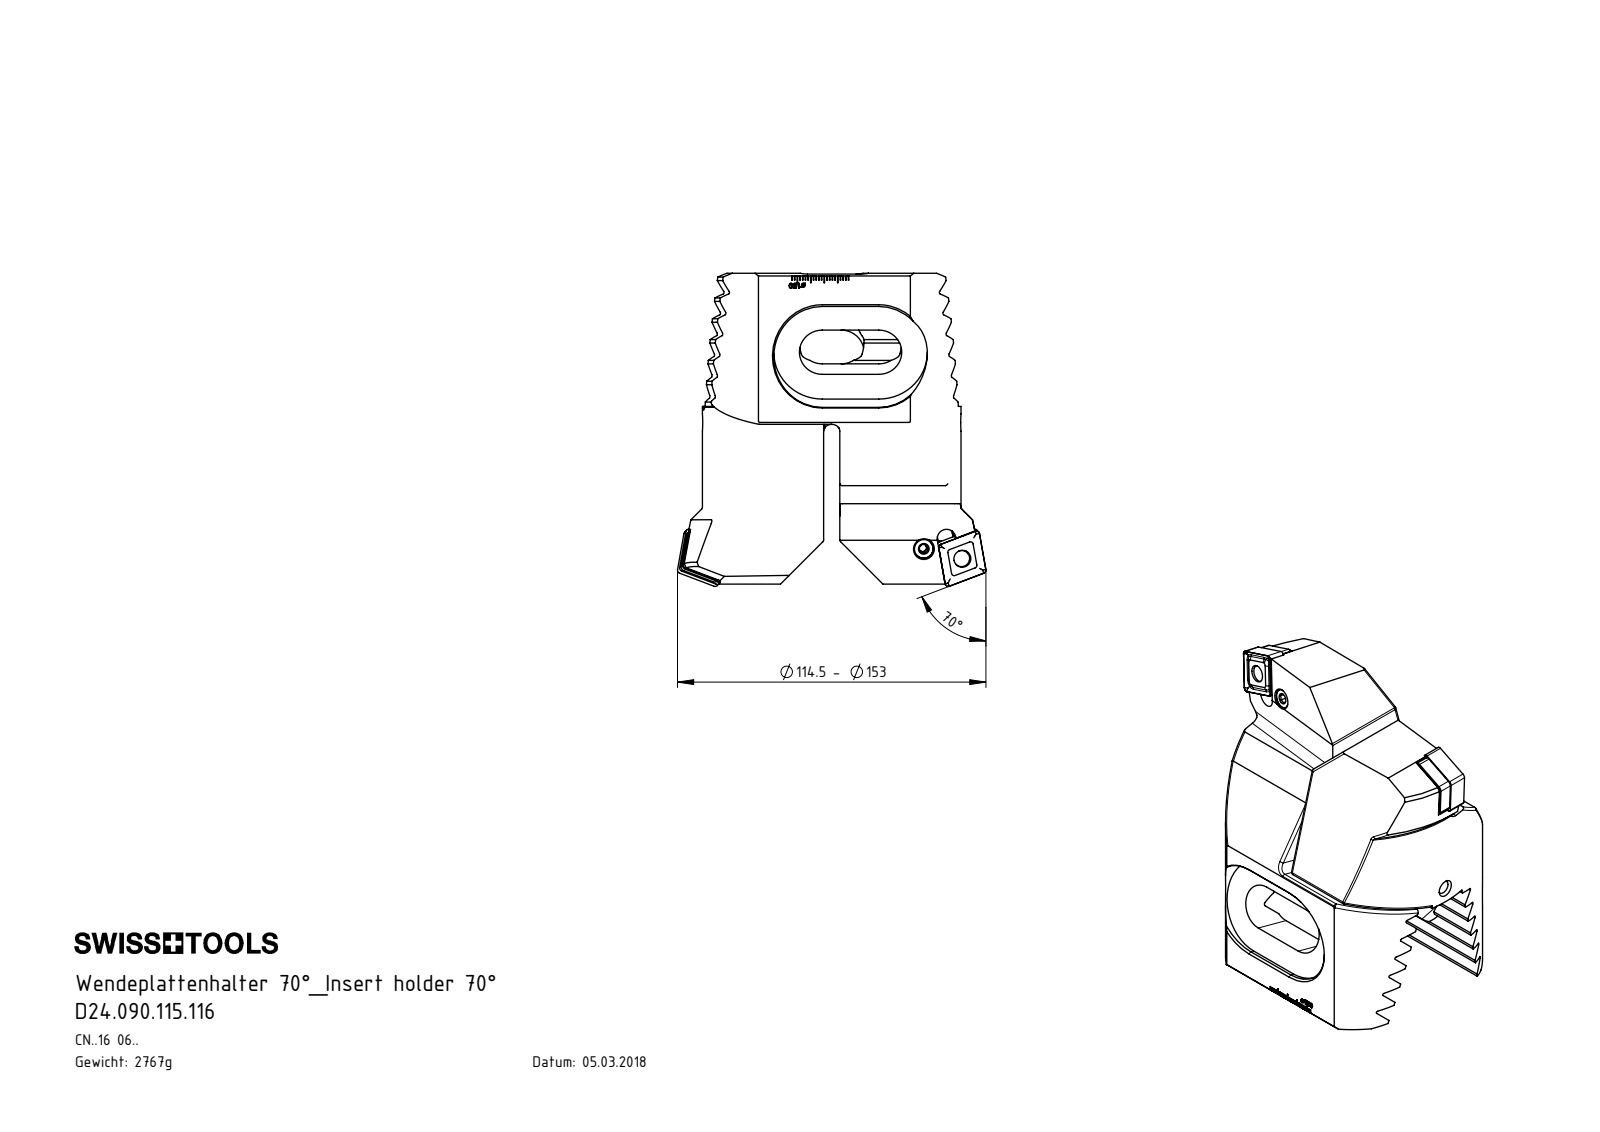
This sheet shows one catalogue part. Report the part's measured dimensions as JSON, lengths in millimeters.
{"part_name": "Z94-xxx.001.067_C_CN 16 70ø; WCE-ER4.101.020_A; WCE-ER3.101.000_A; WCE (+5 more)", "step_written_by": "SolidWorks 2017 (CONFIG_CONTROL_DESIGN)", "units": "millimeters", "bodies": {"solids": 14, "faces": 962, "planar": 536, "cylindrical": 168, "other": 258}, "overall_size": [116.2, 114.5, 75.2], "volume_mm3": 351479, "surface_area_mm2": 70327, "round_holes": [[2, 2], [6.35, 2], [7, 2], [8.05, 2], [8.4, 2], [5, 1]], "round_bosses_or_shafts": [[6, 3], [8, 2], [7.9, 2], [6.4, 2], [3.55, 2], [4, 1]], "partial_cylinders_radius": [[1, 16], [0.58, 12], [1.2, 8], [1.5, 8], [3, 6], [3.5, 6], [0.3, 4], [8.5, 4]], "face_to_face_distances": [6.93, 13.86, 20.79, 27.71, 13.19, 6, 20.78, 1.59, 13.85, 27.72], "hole_center_spacings": [14.78, 15, 25, 48.3]}
